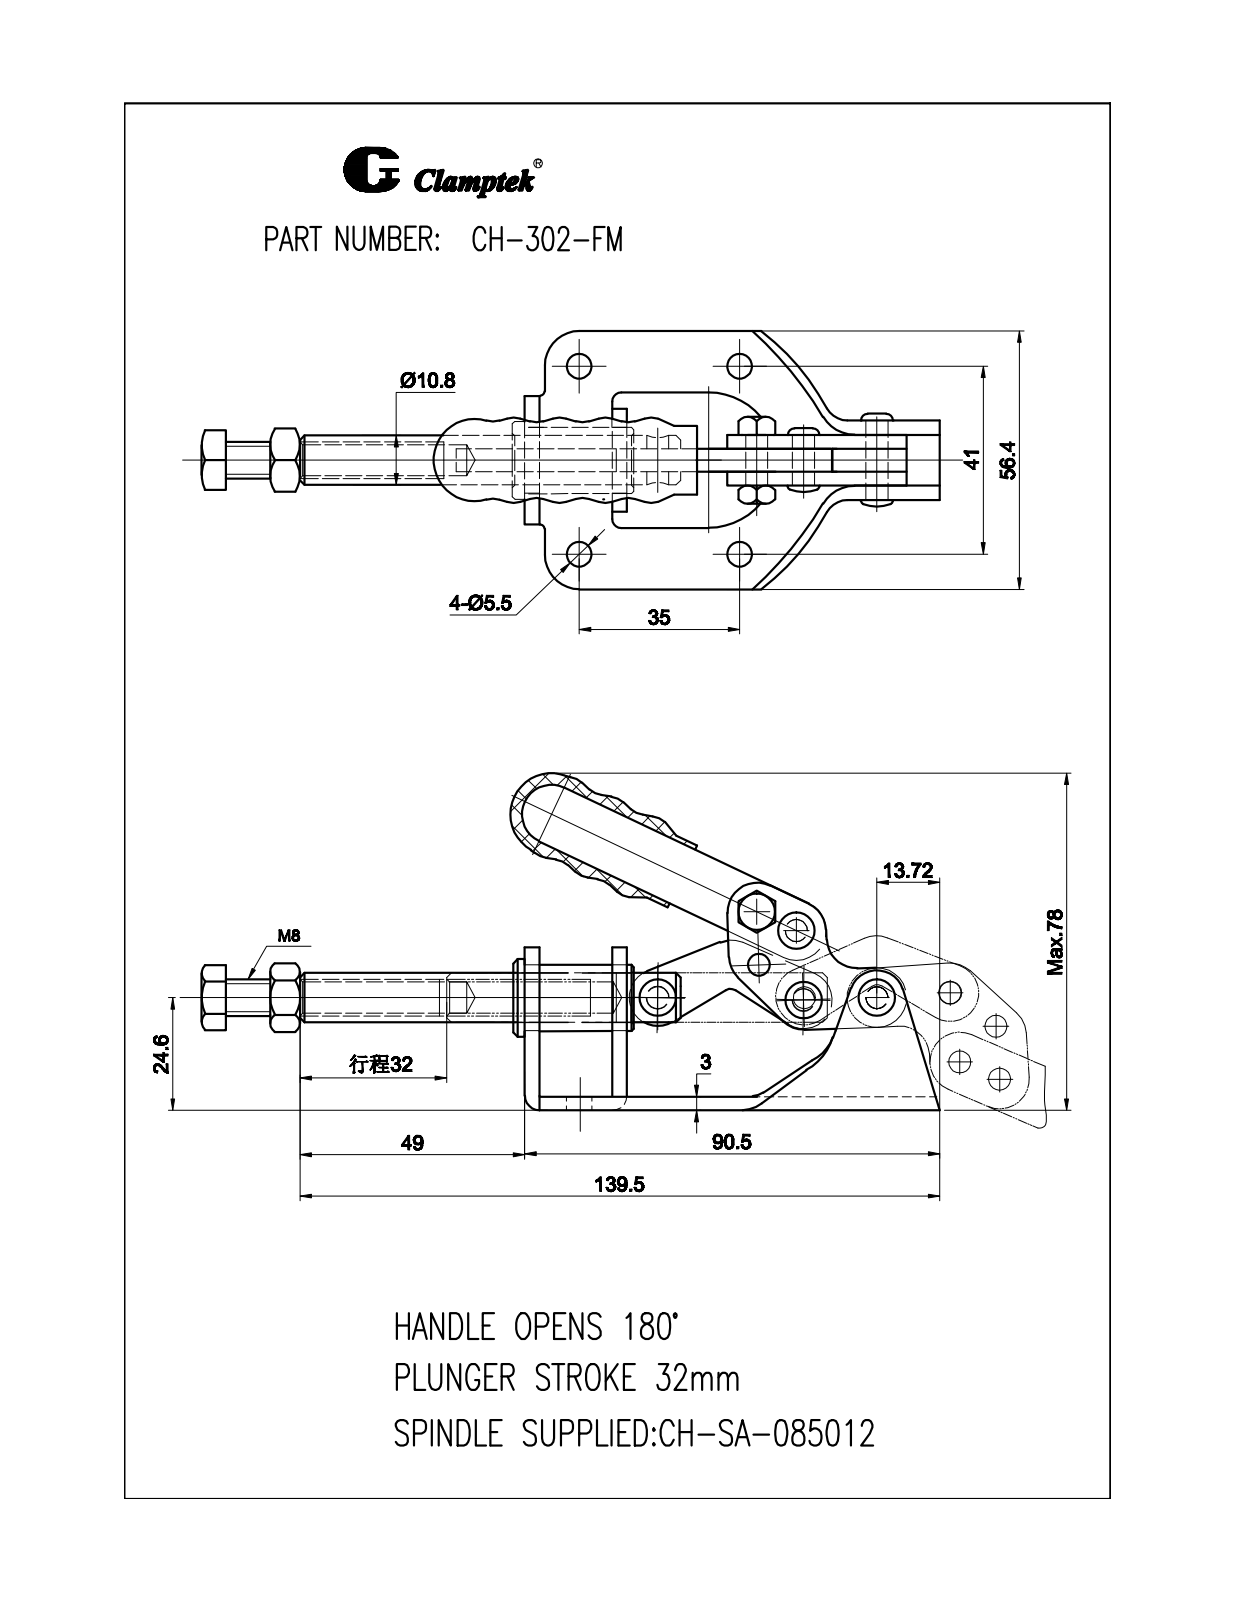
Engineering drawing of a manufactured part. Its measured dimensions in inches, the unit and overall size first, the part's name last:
Units: inches
Overall size (bounding box): 6.369 × 3.139 × 2.219
Round holes (diameter × count): ⌀0.189 ×6, ⌀0.165 ×5, ⌀0.217 ×4, ⌀0.256 ×1, ⌀0.268 ×1, ⌀0.428 ×1, ⌀0.567 ×1
Round bosses / shafts (diameter × count): ⌀0.821 ×1, ⌀0.669 ×1, ⌀0.315 ×1, ⌀0.197 ×1
Partial cylindrical surfaces — rounded edges, fillets, slot ends (radius × count): R0.256 ×8, R0.039 ×3, R0.118 ×2, R0.197 ×2, R0.266 ×2, R0.295 ×2, R0.413 ×2, R0.522 ×2
Main face-to-face distances: 0.118, 0.197, 0.315, 0.217, 0.098, 0.433, 0.236, 0.551, 0.701, 0.335
Hole centre spacings: 1.378, 1.614, 2.122, 0.374, 0.381, 0.396, 0.537, 0.6
Volume: 3.192 in³ · Surface area: 63.13 in²
Bodies: 17 solids, 864 faces (297 planar, 310 cylindrical, 257 other)
Part name (STEP PRODUCT): CH-302-FM-09; M8 Nut; CH-302-FM-06; CH-302-FM-08 (+8 more)
STEP written by: SolidWorks 2010 (CONFIG_CONTROL_DESIGN)
